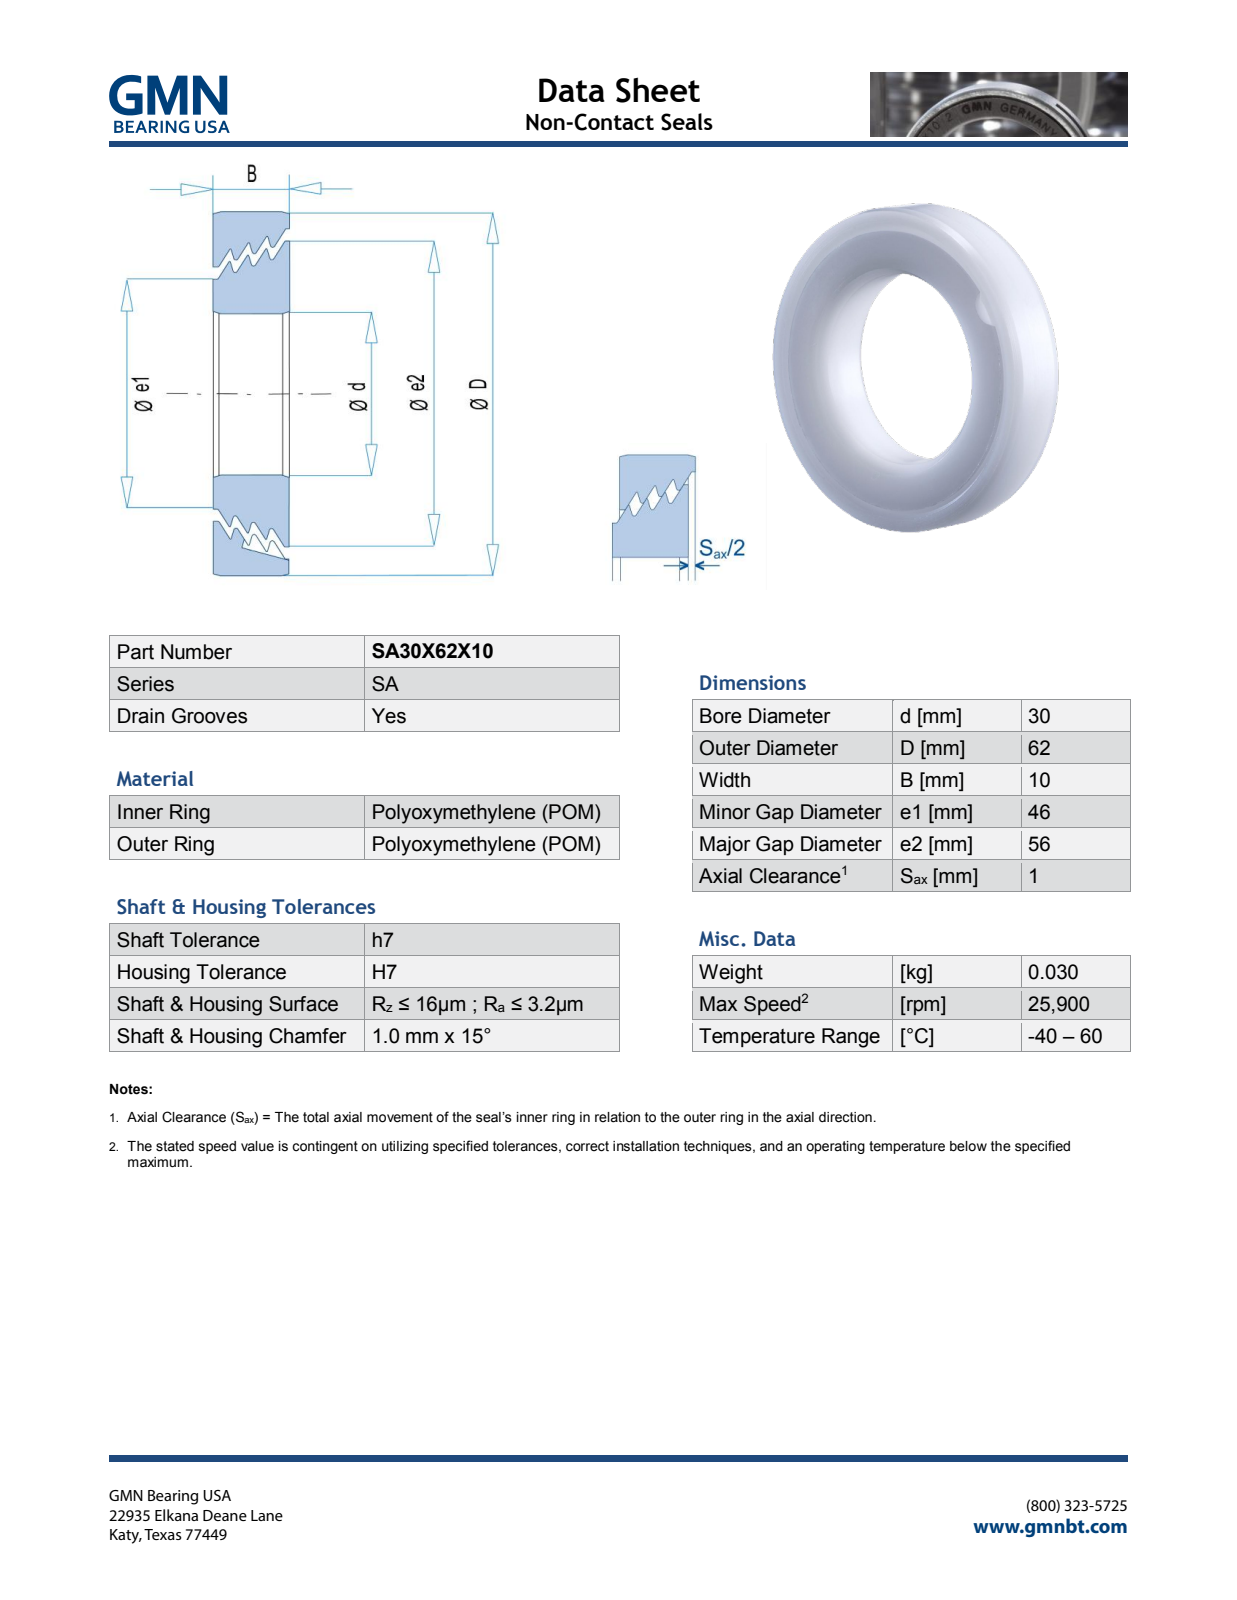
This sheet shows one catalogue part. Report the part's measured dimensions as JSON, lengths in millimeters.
{"part_name": "SA30X62X10_PRT", "step_written_by": "PRO/ENGINEER BY PARAMETRIC TECHNOLOGY CORPORATION, 2013150 (AUTOMOTIVE_DESIGN)", "units": "millimeters", "bodies": {"solids": 2, "faces": 699, "planar": 622, "cylindrical": 15, "other": 62}, "overall_size": [62, 62, 10.07], "volume_mm3": 21689, "surface_area_mm2": 13820, "round_holes": [[30, 1], [47.63, 1], [57.63, 1]], "round_bosses_or_shafts": [[62, 1], [56, 1], [46, 1]], "partial_cylinders_radius": [[6, 1]], "face_to_face_distances": [10, 10.07, 0.45, 3.63, 0.46, 3.18, 3.17, 0.41, 3.64, 2.73]}
